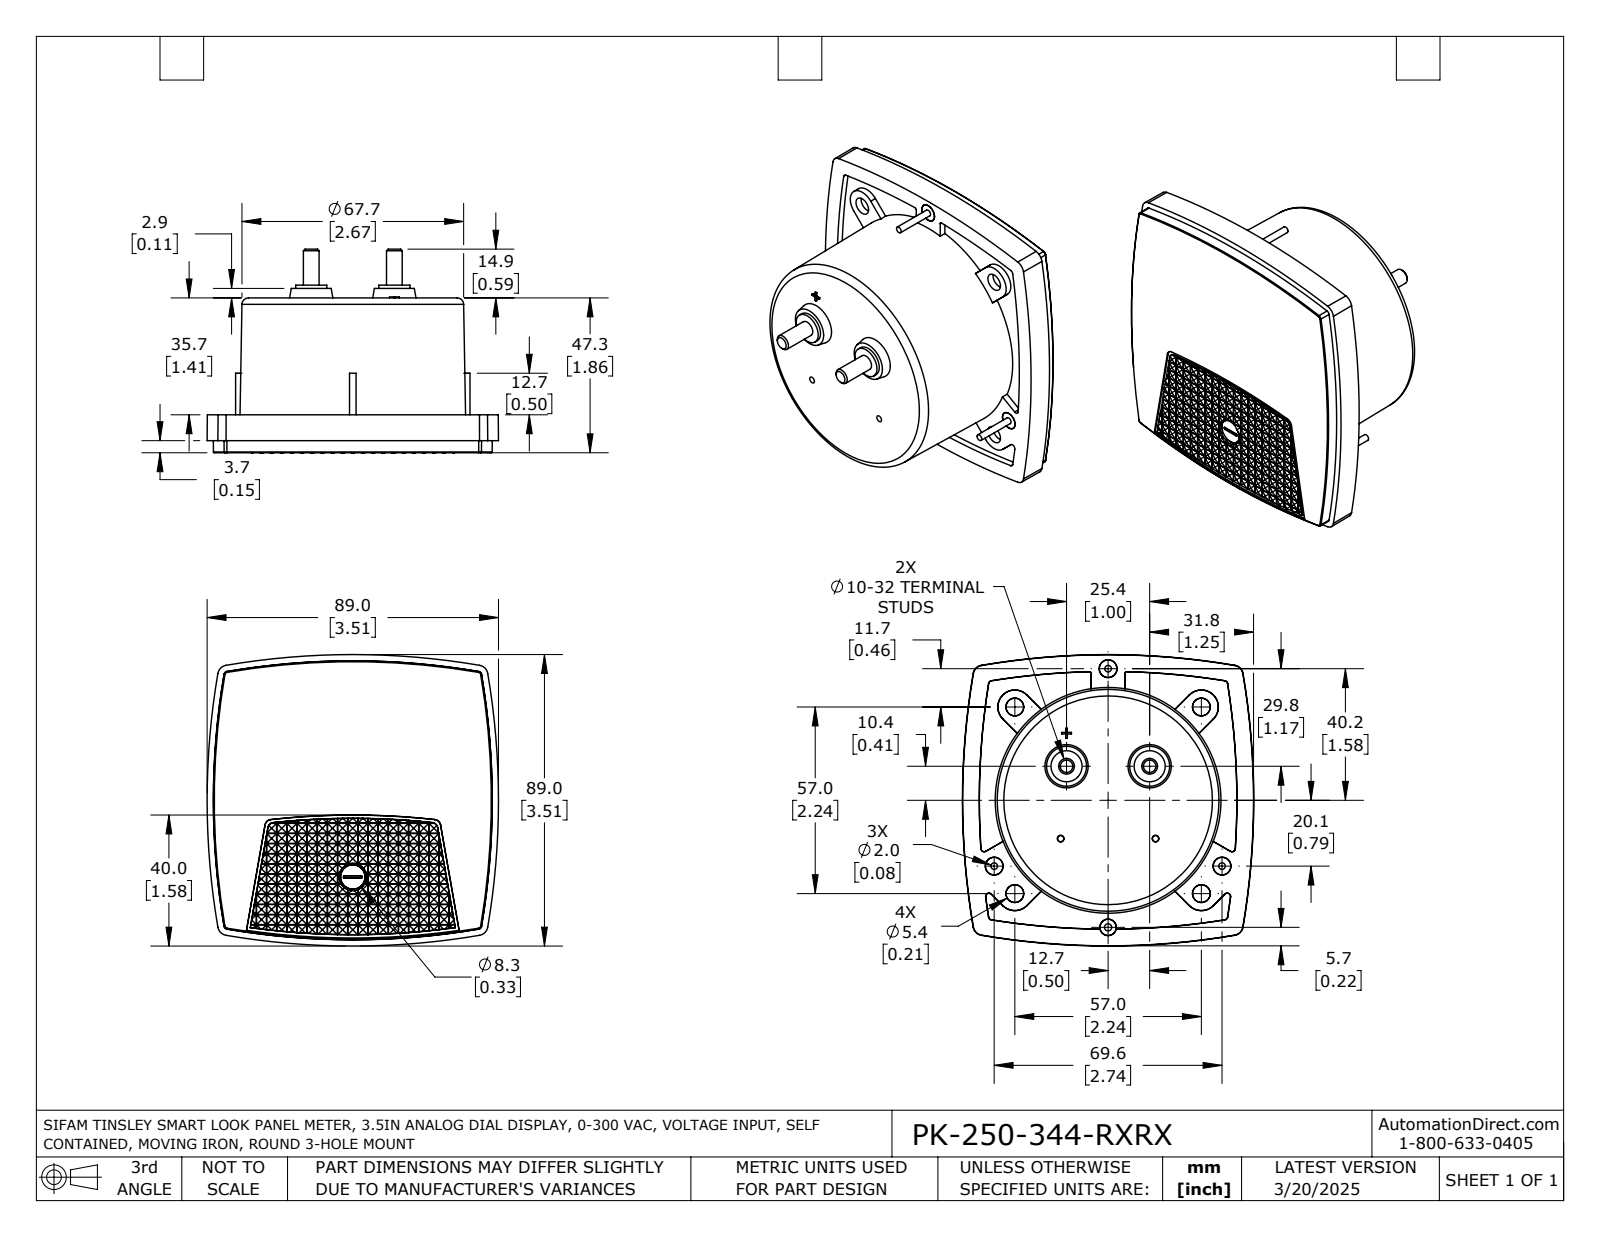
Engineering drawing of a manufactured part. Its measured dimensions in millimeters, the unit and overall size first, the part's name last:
Units: millimetres
Overall size (bounding box): 89 × 89 × 62.3
Round holes (diameter × count): ⌀2.2 ×1
Round bosses / shafts (diameter × count): ⌀5.4 ×3, ⌀2 ×3, ⌀9.5 ×2, ⌀4.8 ×2
Partial cylindrical surfaces — rounded edges, fillets, slot ends (radius × count): R227.6 ×1
Main face-to-face distances: 47.3, 35.7, 11.6, 2, 37.7, 9.6, 0.6, 2.4, 1.8, 3
Volume: 212 900 mm³ · Surface area: 28 570 mm²
Bodies: 1 solid, 1078 faces (950 planar, 23 cylindrical, 105 other)
Part name (STEP PRODUCT): PK-250-344-RXRX
STEP written by: SolidWorks 2021 (AUTOMOTIVE_DESIGN)
